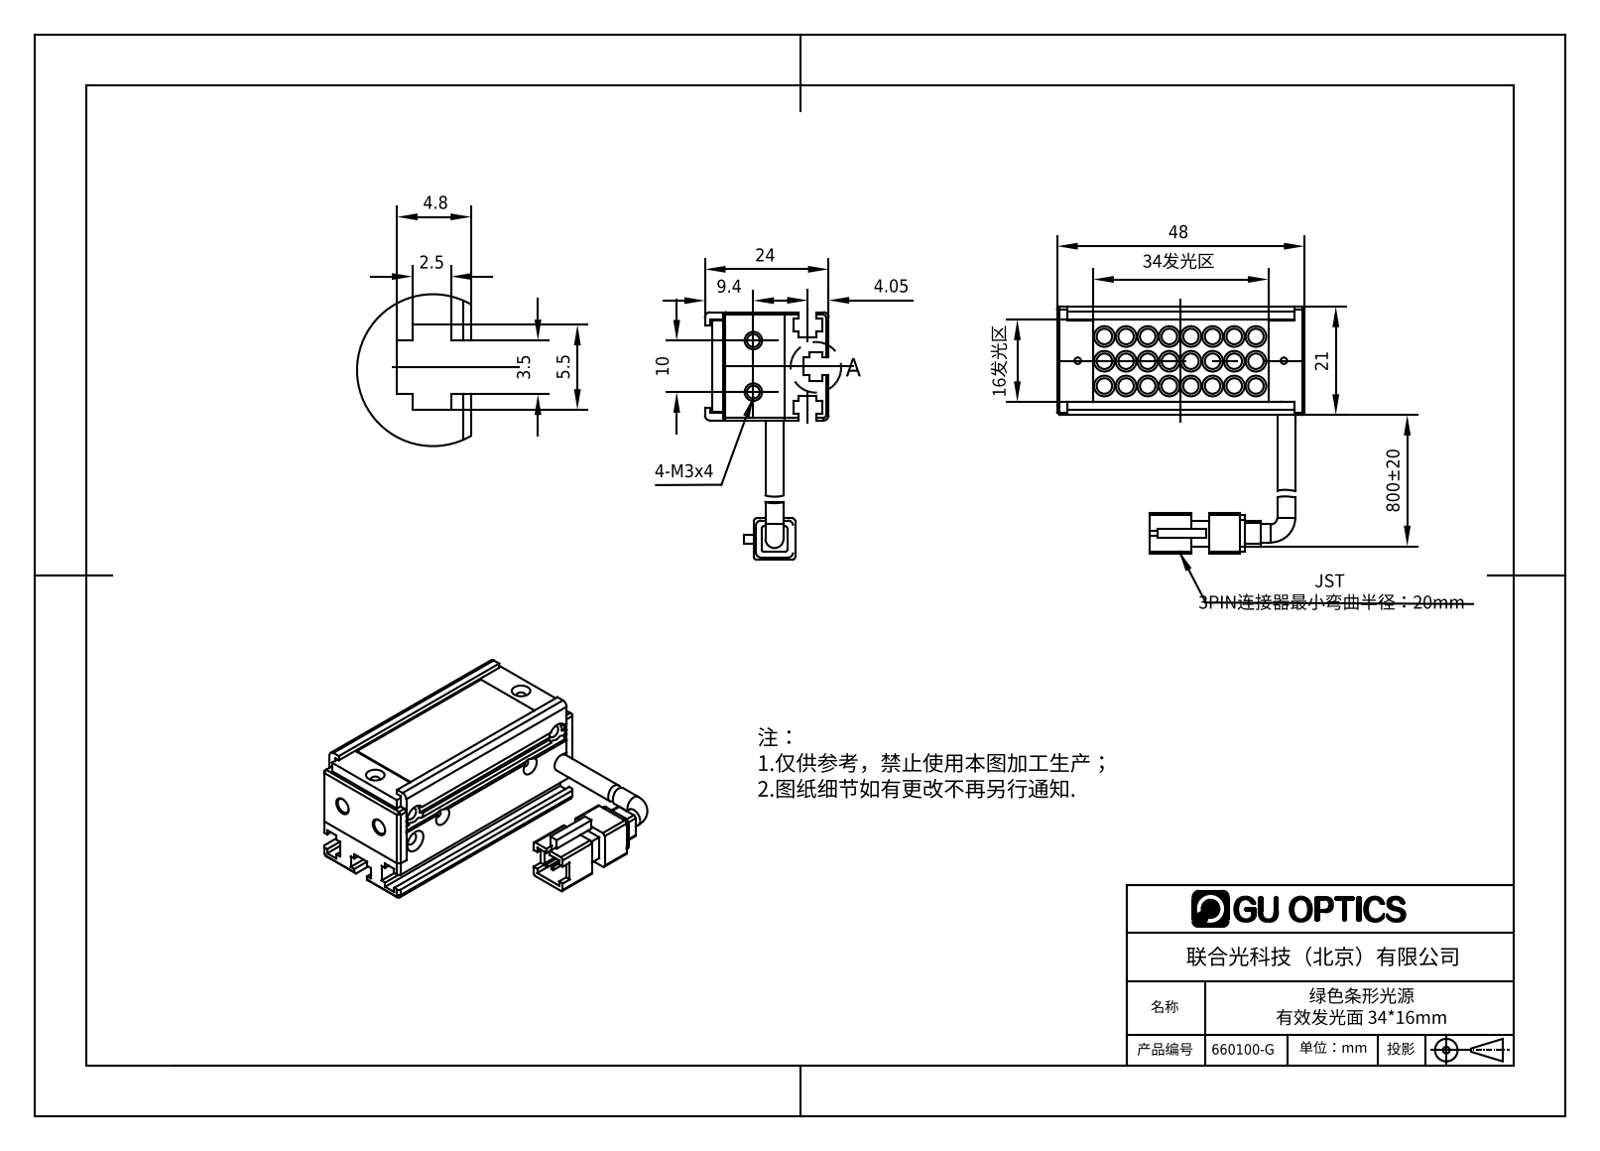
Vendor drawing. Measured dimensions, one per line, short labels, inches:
name: 660100-G
written by: SolidWorks 2016 (AUTOMOTIVE_DESIGN)
unit: in
bodies: 6 solids, 878 faces (536 planar, 193 cylindrical, 149 other)
size: 1.89 × 1.89 × 0.945
volume: 0.946 in³; area: 24.88 in²
holes: 4× ⌀0.049, 4× ⌀0.063, 4× ⌀0.094, 2× ⌀0.067, 2× ⌀0.098, 2× ⌀0.118, 1× ⌀0.079
bosses: 24× ⌀0.157, 24× ⌀0.118, 2× ⌀0.138
rounds: 12× R0.039, 8× R0.02, 4× R0.039, 1× R0.065
face distances: 0.039, 0.098, 0.079, 0.728, 0.807, 0.051, 0.138, 0.472, 0.335, 0.618
hole spacings: 0.236, 0.307, 0.333, 1.243, 1.25, 1.535, 1.554, 0.394
